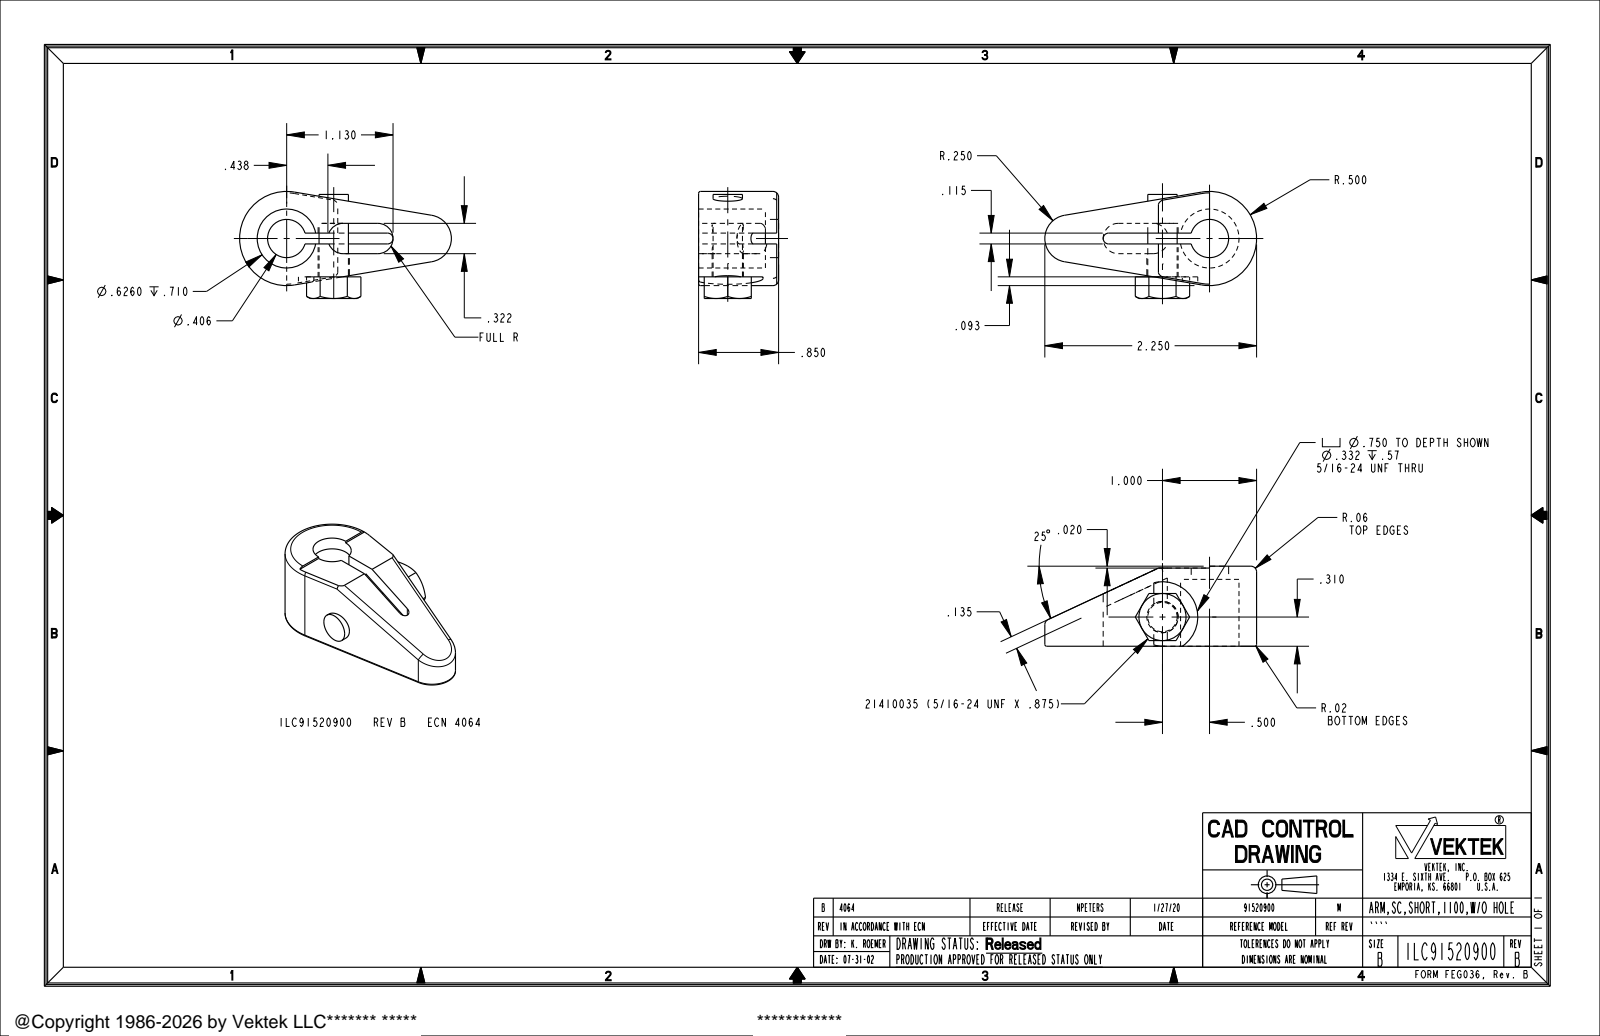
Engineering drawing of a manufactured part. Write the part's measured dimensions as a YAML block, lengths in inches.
part_name: "ILC91520900"
step_written_by: "PRO/ENGINEER BY PARAMETRIC TECHNOLOGY CORPORATION, 2013320 (AUTOMOTIVE_DESIGN)"
units: inches
bodies: {solids: 1, faces: 61, planar: 26, cylindrical: 25, other: 10}
overall_size: [2.25, 1.137, 0.85]
volume: 0.861
surface_area: 10.55
round_holes:
  - {diameter: 0.332, count: 1}
  - {diameter: 0.406, count: 1}
  - {diameter: 0.626, count: 1}
round_bosses_or_shafts:
  - {diameter: 0.312, count: 1}
partial_cylinders:
  - {radius: 0.06, count: 4}
  - {radius: 0.02, count: 2}
  - {radius: 0.161, count: 2}
  - {radius: 0.057, count: 1}
  - {radius: 0.25, count: 1}
  - {radius: 0.375, count: 1}
  - {radius: 0.5, count: 1}
face_to_face_distances: [0.104, 0.219, 0.83, 0.85, 0.02, 0.322, 0.476, 0.798, 0.58, 0.694]
